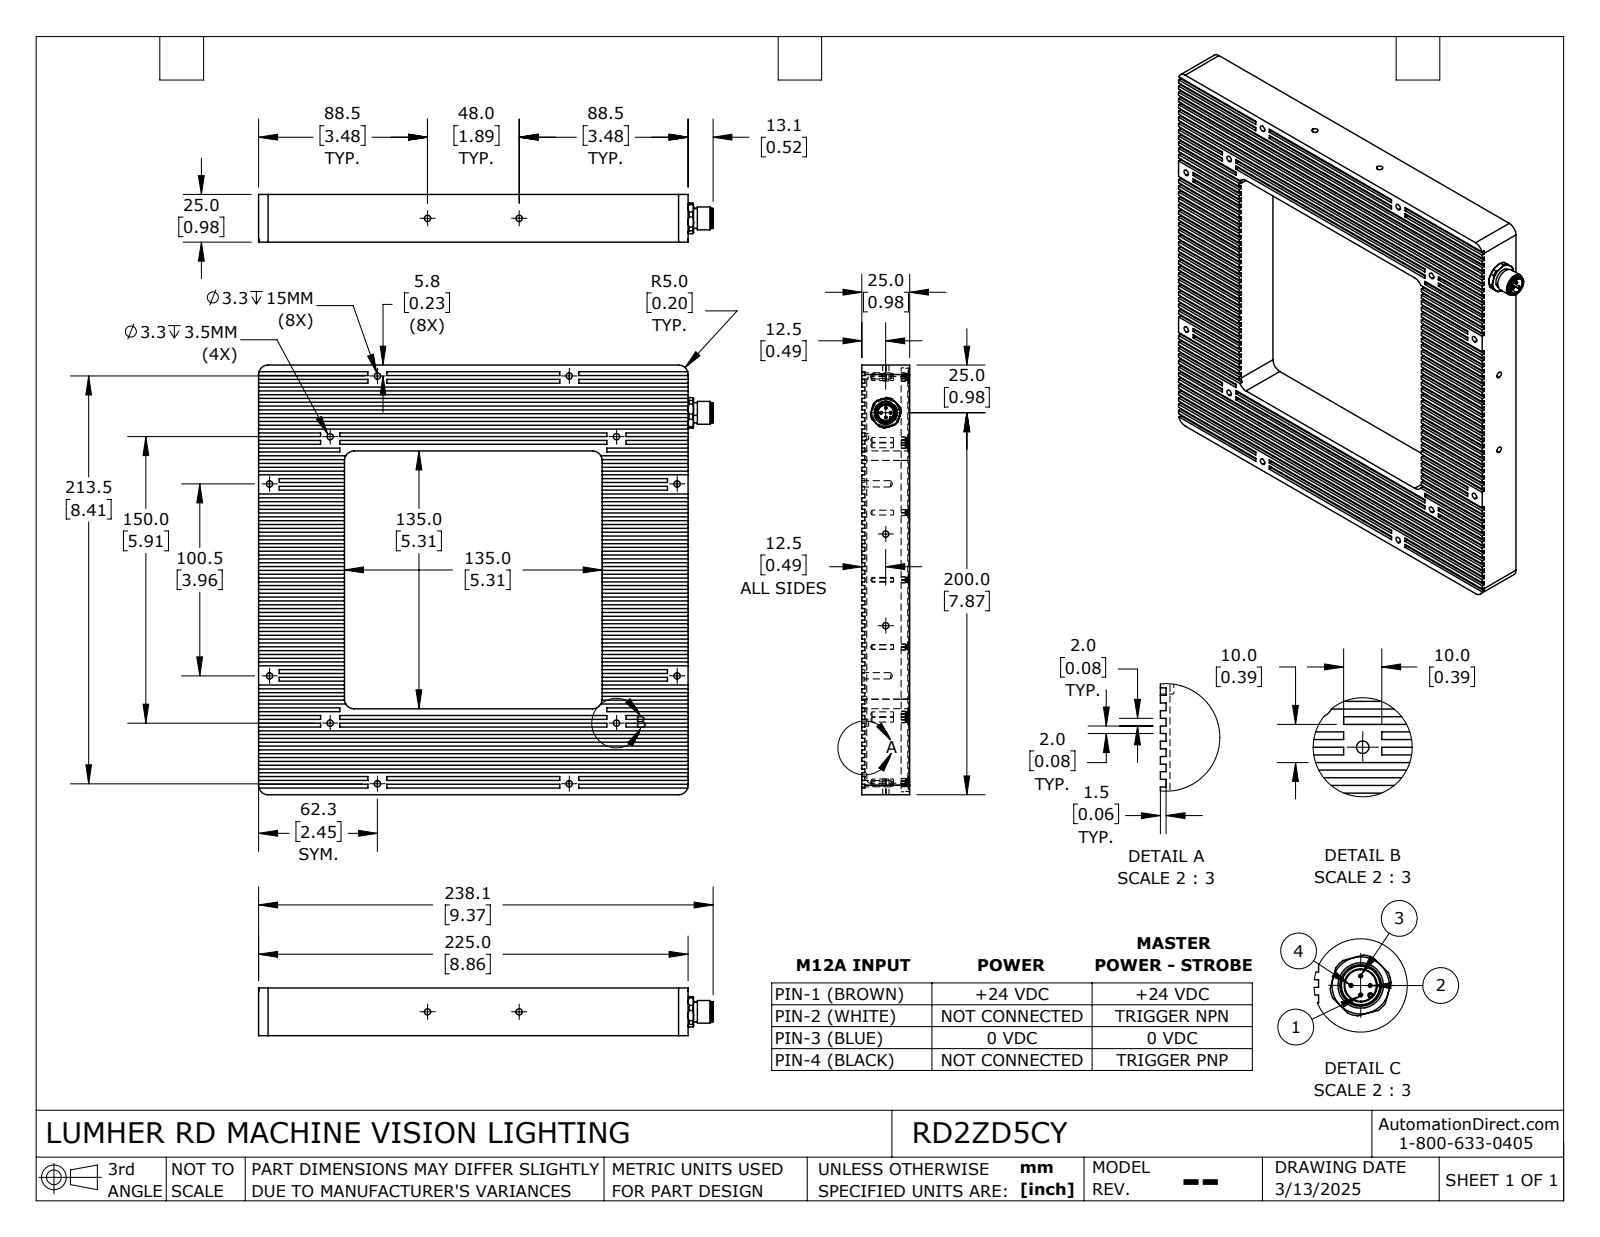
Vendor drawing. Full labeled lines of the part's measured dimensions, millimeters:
Part name (STEP PRODUCT): RD2ZD5CY
STEP written by: SolidWorks 2024 (AUTOMOTIVE_DESIGN)
Units: millimetres
Bodies: 1 solid, 3276 faces (670 planar, 1729 cylindrical, 877 other)
Overall size (bounding box): 238.1 × 225 × 25
Volume: 766 576 mm³ · Surface area: 145 055 mm²
Round holes (diameter × count): ⌀3.2 ×40, ⌀2.5 ×38, ⌀3.3 ×16, ⌀1.45 ×4, ⌀8.3 ×1, ⌀9.4 ×1, ⌀11 ×1, ⌀12.2 ×1
Round bosses / shafts (diameter × count): ⌀5.6 ×40, ⌀3 ×40, ⌀0.8 ×40, ⌀1.4 ×4, ⌀1 ×4, ⌀11.91 ×1, ⌀11.9 ×1, ⌀10.6 ×1
Partial cylindrical surfaces — rounded edges, fillets, slot ends (radius × count): R0.57 ×480, R0.25 ×240, R1.02 ×40, R5 ×8, R2 ×4, R3.3 ×4, R3.5 ×4, R6.5 ×4
Main face-to-face distances: 1.5, 24.5, 180, 23, 45, 43.5, 135, 225, 43.3, 1.7
Hole centre spacings: 40.26, 129.21, 166.86, 183.43, 220.73, 55.34, 155.83, 183.15
